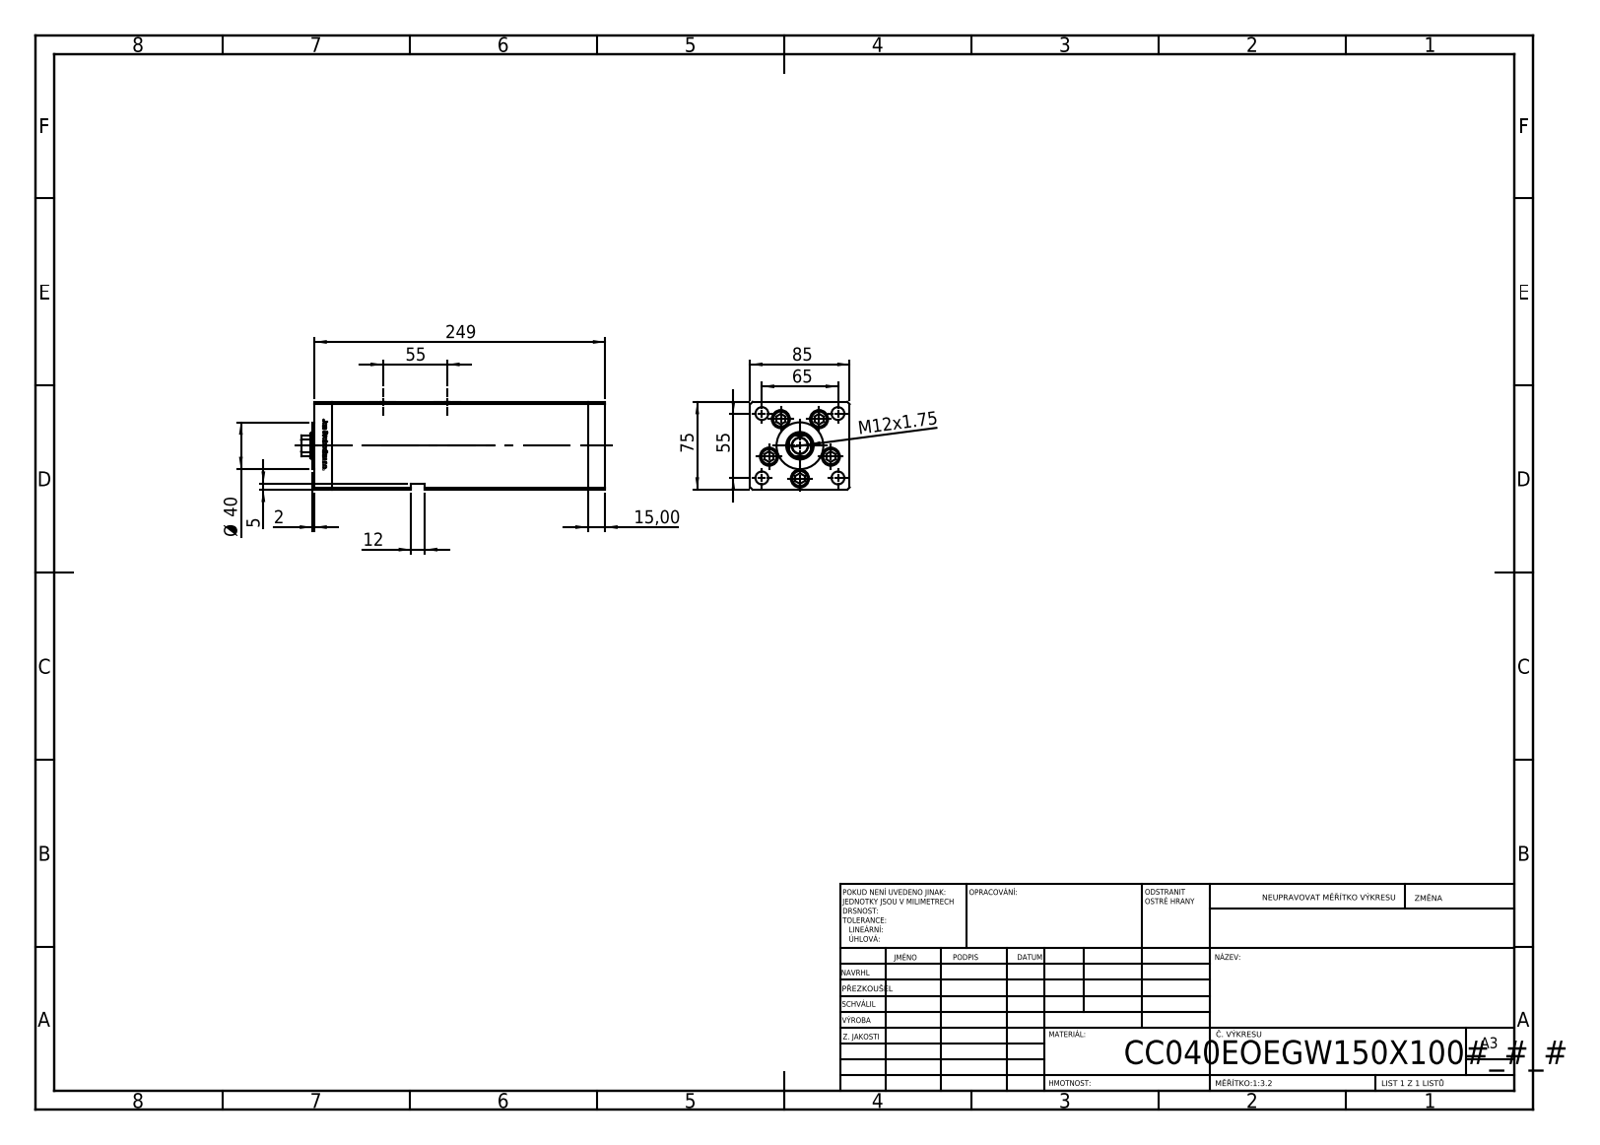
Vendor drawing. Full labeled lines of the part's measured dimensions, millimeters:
Part name (STEP PRODUCT): V220C_E MIDDLE; V220C_VC_E; V220C BACK_E; V220C_FRONT_E (+1 more)
STEP written by: SolidWorks 2019 (CONFIG_CONTROL_DESIGN)
Units: millimetres
Bodies: 14 solids, 1214 faces (475 planar, 165 cylindrical, 574 other)
Overall size (bounding box): 260 × 85 × 75
Volume: 1 341 000 mm³ · Surface area: 209 571 mm²
Round holes (diameter × count): ⌀11 ×9, ⌀15.5 ×5, ⌀10.5 ×4, ⌀16.5 ×4, ⌀2 ×2, ⌀13.16 ×2, ⌀13.5 ×1, ⌀22 ×1, ⌀23.5 ×1
Round bosses / shafts (diameter × count): ⌀14.5 ×5, ⌀8 ×5, ⌀40 ×1
Partial cylindrical surfaces — rounded edges, fillets, slot ends (radius × count): R0.93 ×2, R10.5 ×1
Main face-to-face distances: 85, 75, 15, 218.5, 233.5, 248.5, 10.5, 64.5, 34.25, 68.5
Hole centre spacings: 28, 42.57, 55, 65, 85.15, 16.86, 19.17, 32.33
